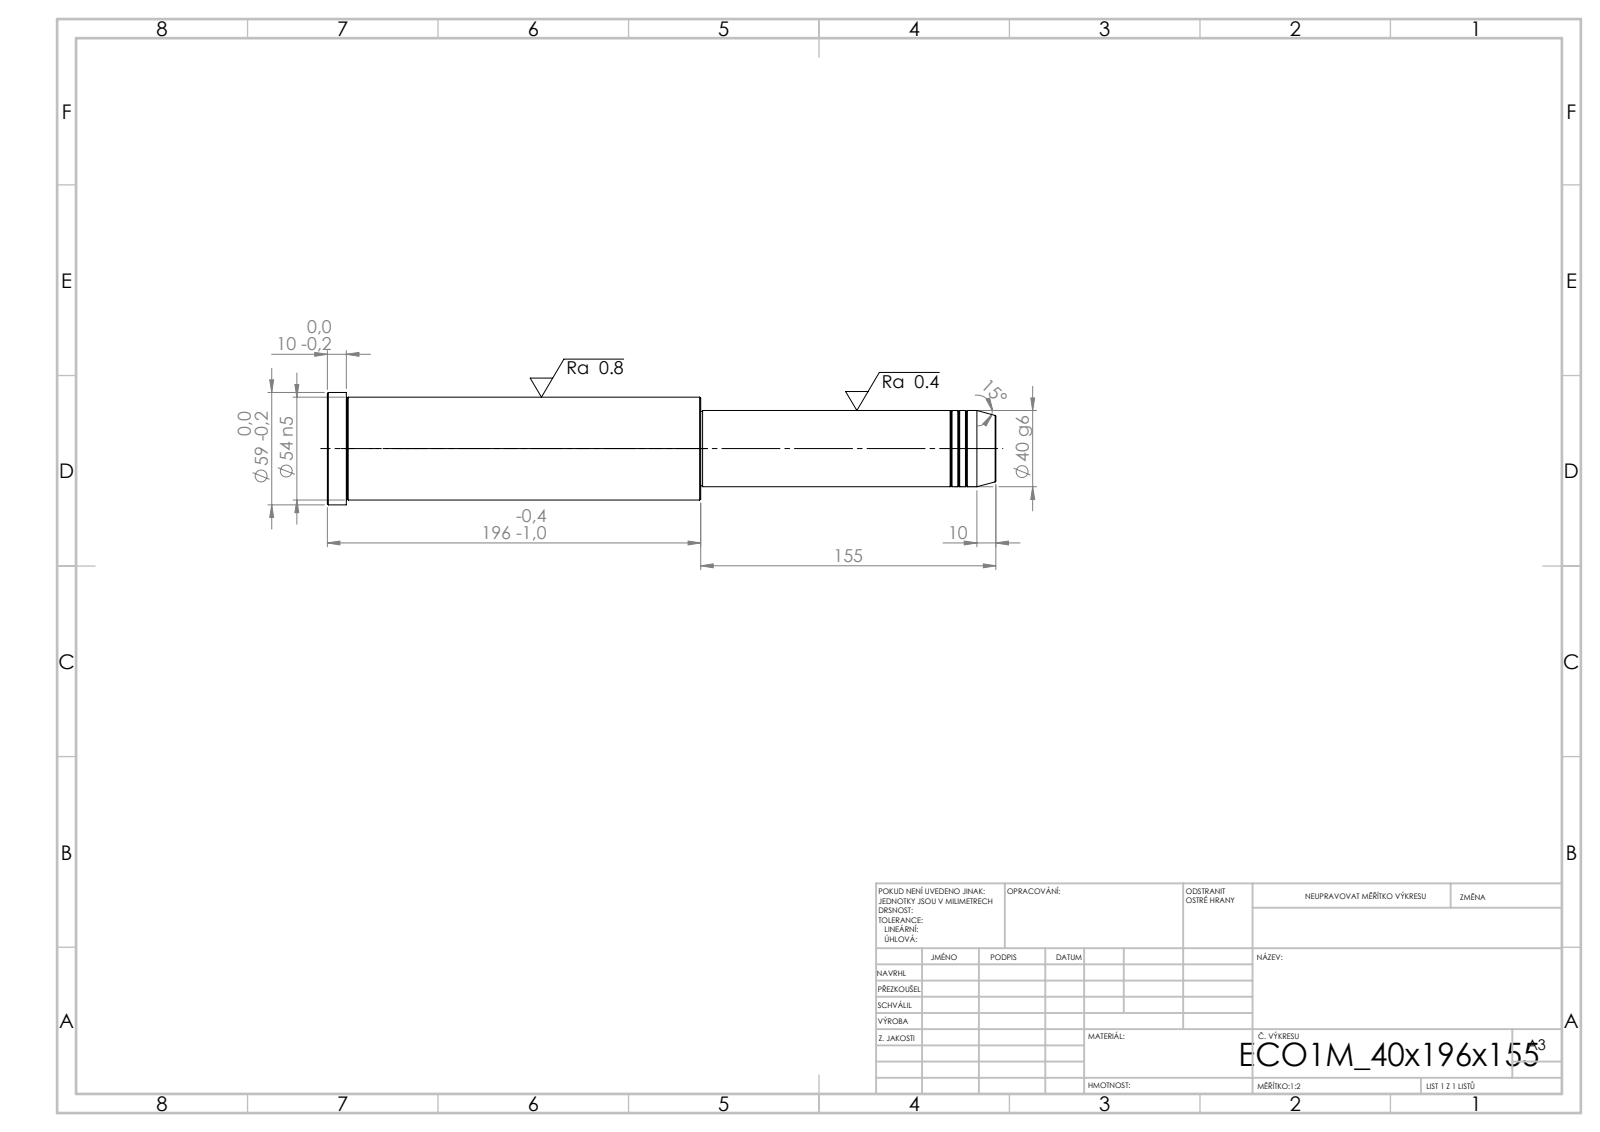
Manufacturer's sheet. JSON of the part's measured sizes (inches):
{"step_written_by": "SolidWorks 2019 (CONFIG_CONTROL_DESIGN)", "units": "inches", "bodies": {"solids": 1, "faces": 43, "planar": 5, "cylindrical": 14, "other": 24}, "overall_size": [13.819, 2.323, 2.323], "volume_in3": 39.43, "surface_area_in2": 90.37, "round_bosses_or_shafts": [[2.323, 1], [2.126, 1], [1.575, 1], [1.535, 1]], "face_to_face_distances": [7.717, 6.102, 13.819, 13.425, 7.323, 0.394, 6.063, 0.039, 7.362, 7.756]}
